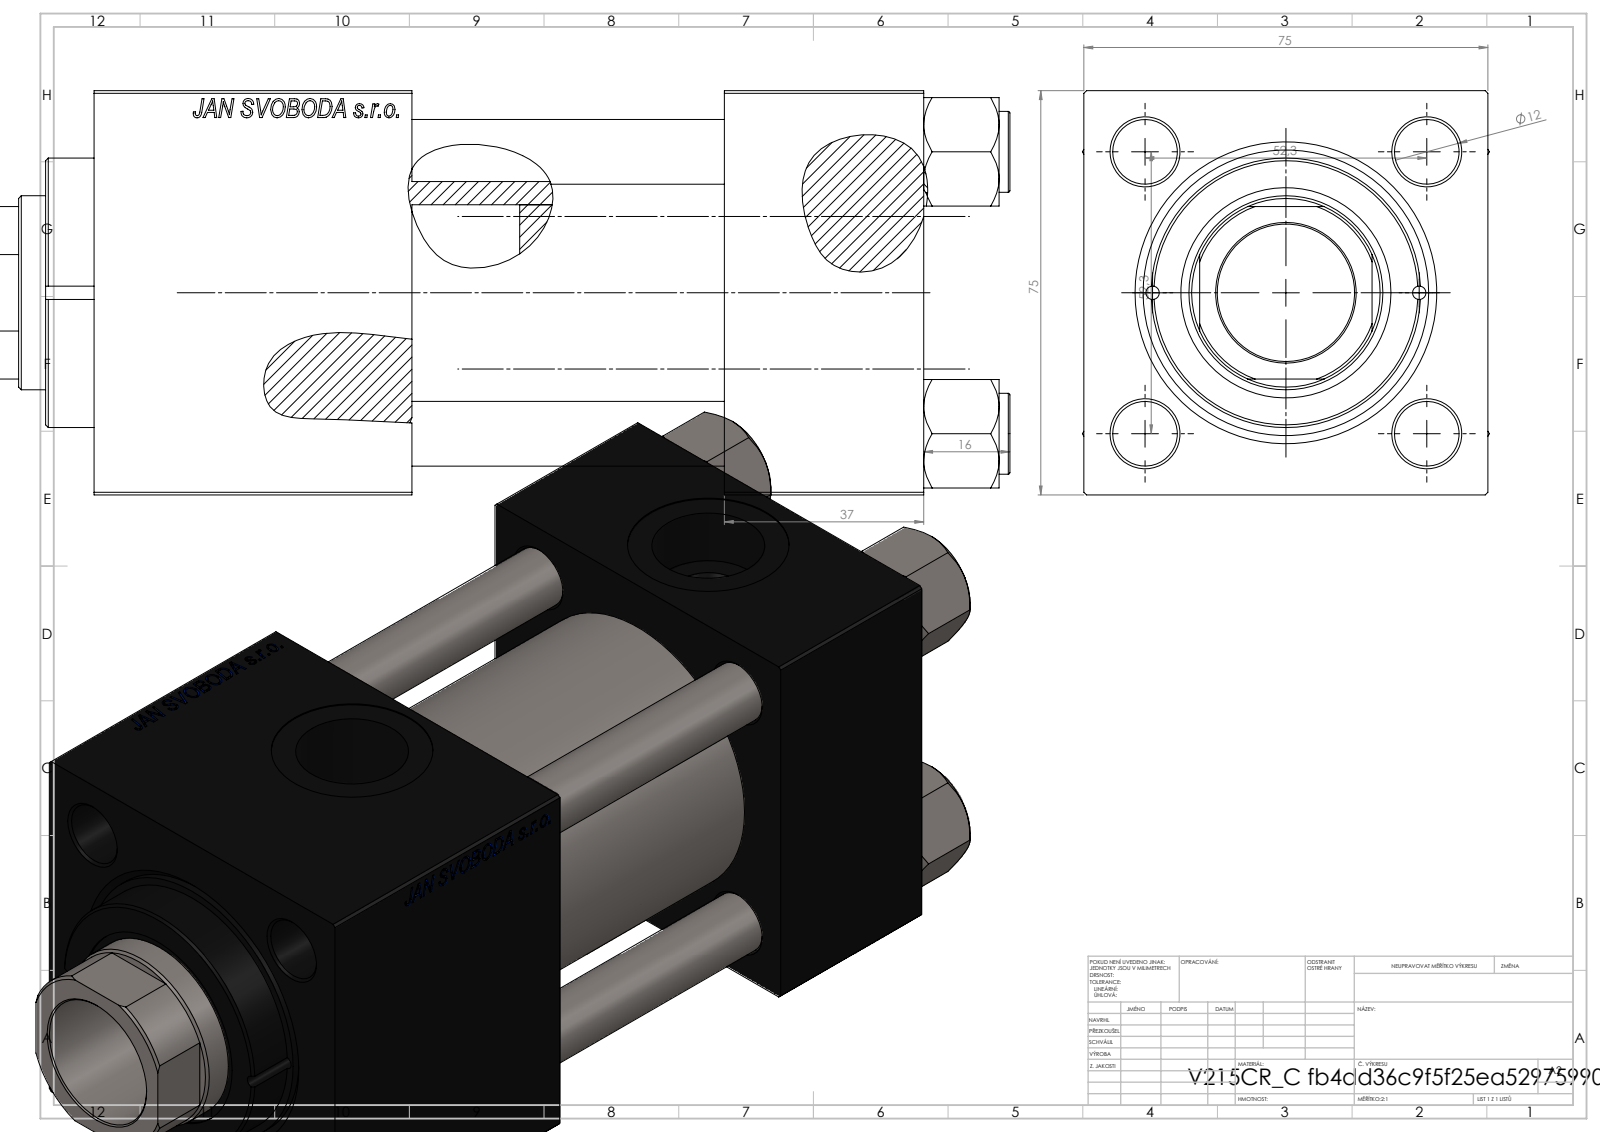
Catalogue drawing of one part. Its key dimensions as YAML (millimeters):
part_name: "V215CR_C_Body; V215CR_VCP_C; V215CR_C_TYCINKA; NUT_M5_C (+1 more)"
step_written_by: "SolidWorks 2019 (CONFIG_CONTROL_DESIGN)"
units: millimeters
bodies: {solids: 11, faces: 1155, planar: 528, cylindrical: 91, other: 536}
overall_size: [195, 75.54, 75]
volume: 685818
surface_area: 155609
round_holes:
  - {diameter: 12, count: 4}
  - {diameter: 2.5, count: 2}
  - {diameter: 7, count: 2}
  - {diameter: 20.96, count: 2}
  - {diameter: 30, count: 2}
  - {diameter: 25.5, count: 1}
  - {diameter: 36, count: 1}
  - {diameter: 39, count: 1}
  - {diameter: 41, count: 1}
  - {diameter: 53, count: 1}
round_bosses_or_shafts:
  - {diameter: 15, count: 4}
  - {diameter: 56, count: 1}
  - {diameter: 50, count: 1}
partial_cylinders:
  - {radius: 17.5, count: 1}
face_to_face_distances: [75, 37, 95, 58, 59, 154, 117, 125.3, 88.3, 30.3]
hole_center_spacings: [26.19, 36.98, 52.3, 57.22, 24.75, 73.96, 49.5, 93.5]
